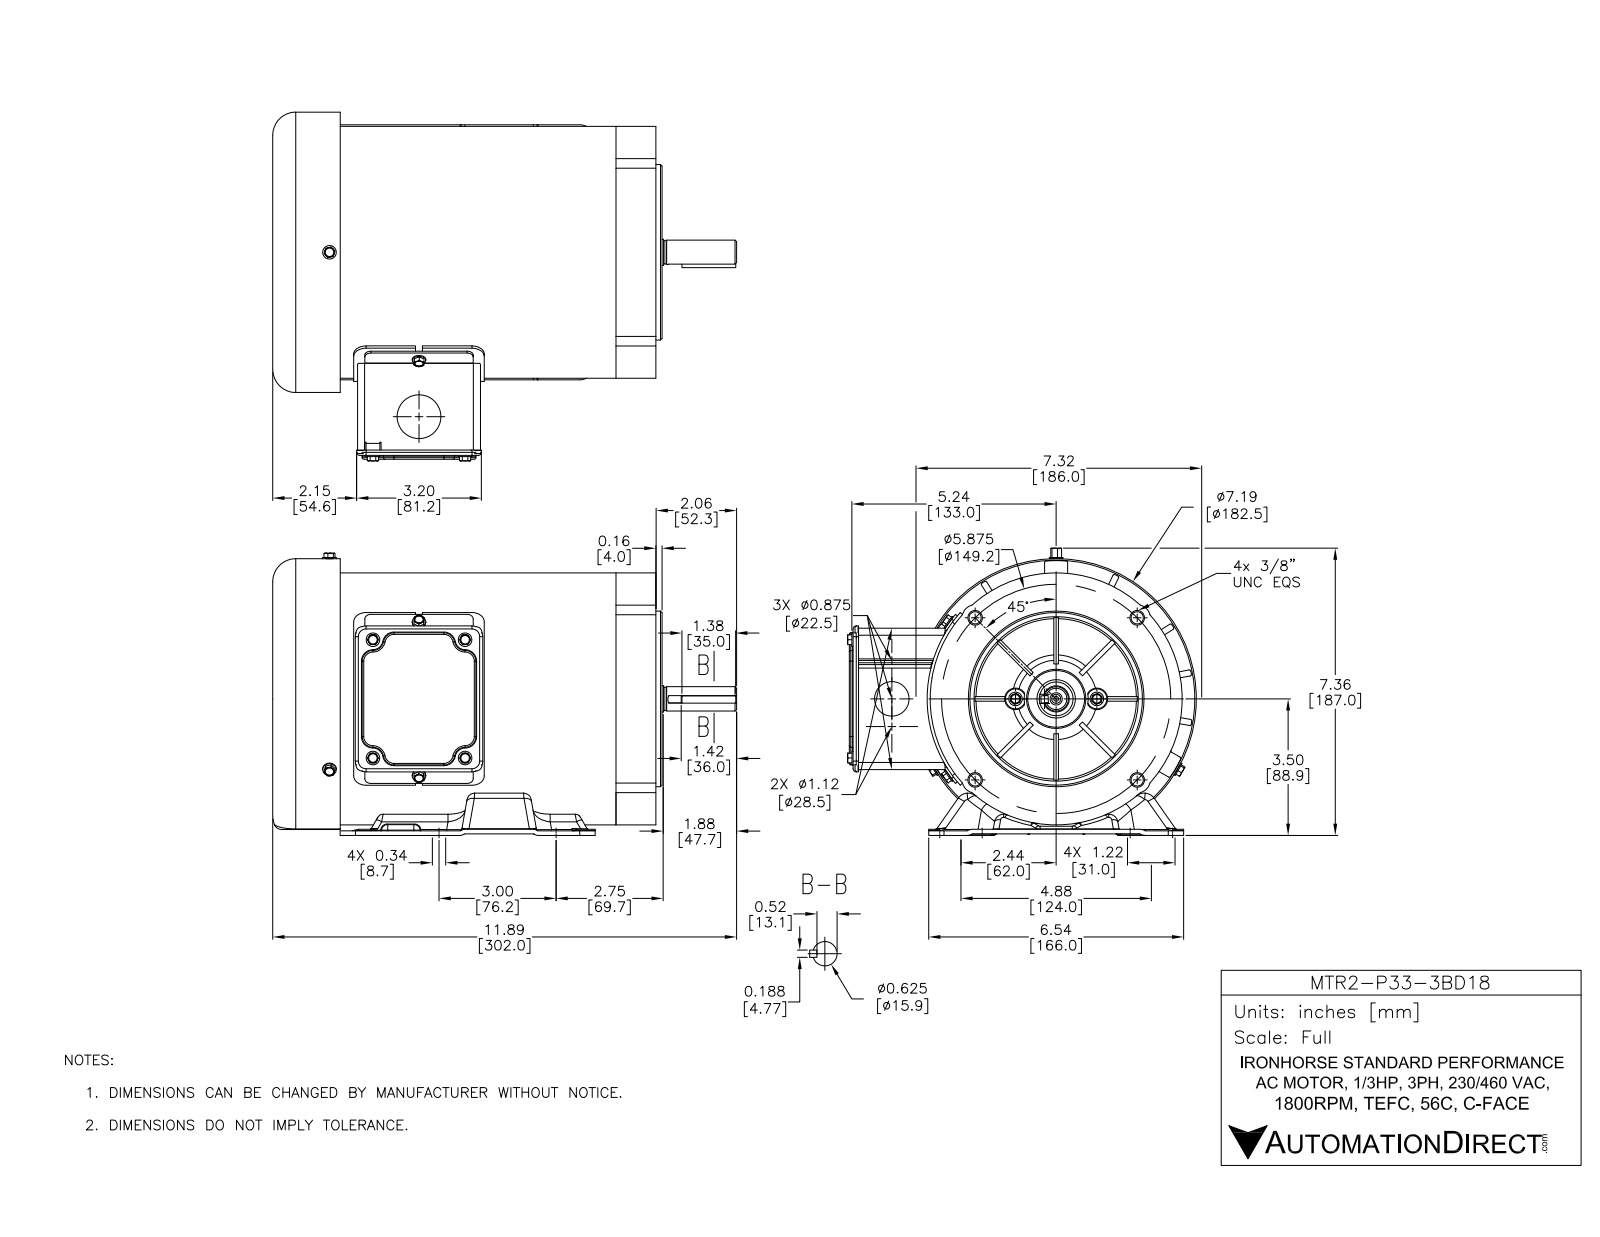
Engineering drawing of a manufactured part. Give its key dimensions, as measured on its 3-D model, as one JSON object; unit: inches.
{"part_name": "MTR2-P33-3BD18", "step_written_by": "SolidWorks 2016 (AUTOMOTIVE_DESIGN)", "units": "inches", "bodies": {"solids": 37, "faces": 2761, "planar": 763, "cylindrical": 888, "other": 1110}, "overall_size": [11.634, 8.938, 7.234], "volume_in3": 48.55, "surface_area_in2": 976.3, "round_holes": [[0.197, 12], [0.219, 11], [0.276, 8], [0.217, 6], [0.344, 6], [0.136, 5], [0.15, 4], [0.177, 4], [0.313, 4], [0.067, 2], [0.134, 2], [0.512, 2]], "round_bosses_or_shafts": [[0.164, 11], [0.348, 7], [0.25, 6], [0.348, 4], [7.185, 1], [6.457, 1], [4.5, 1], [0.945, 1]], "partial_cylinders_radius": [[0.118, 121], [0.039, 38], [0.02, 32], [0.157, 32], [0.138, 26], [0.276, 19], [0.172, 12], [0.197, 12]], "face_to_face_distances": [0.118, 0.039, 0.063, 8.386, 1.024, 1.142, 9.528, 9.567, 3.559, 0.079], "hole_center_spacings": [4.221, 3.031, 0.094, 2.32, 2.409, 2.937, 2.979, 3.748]}
